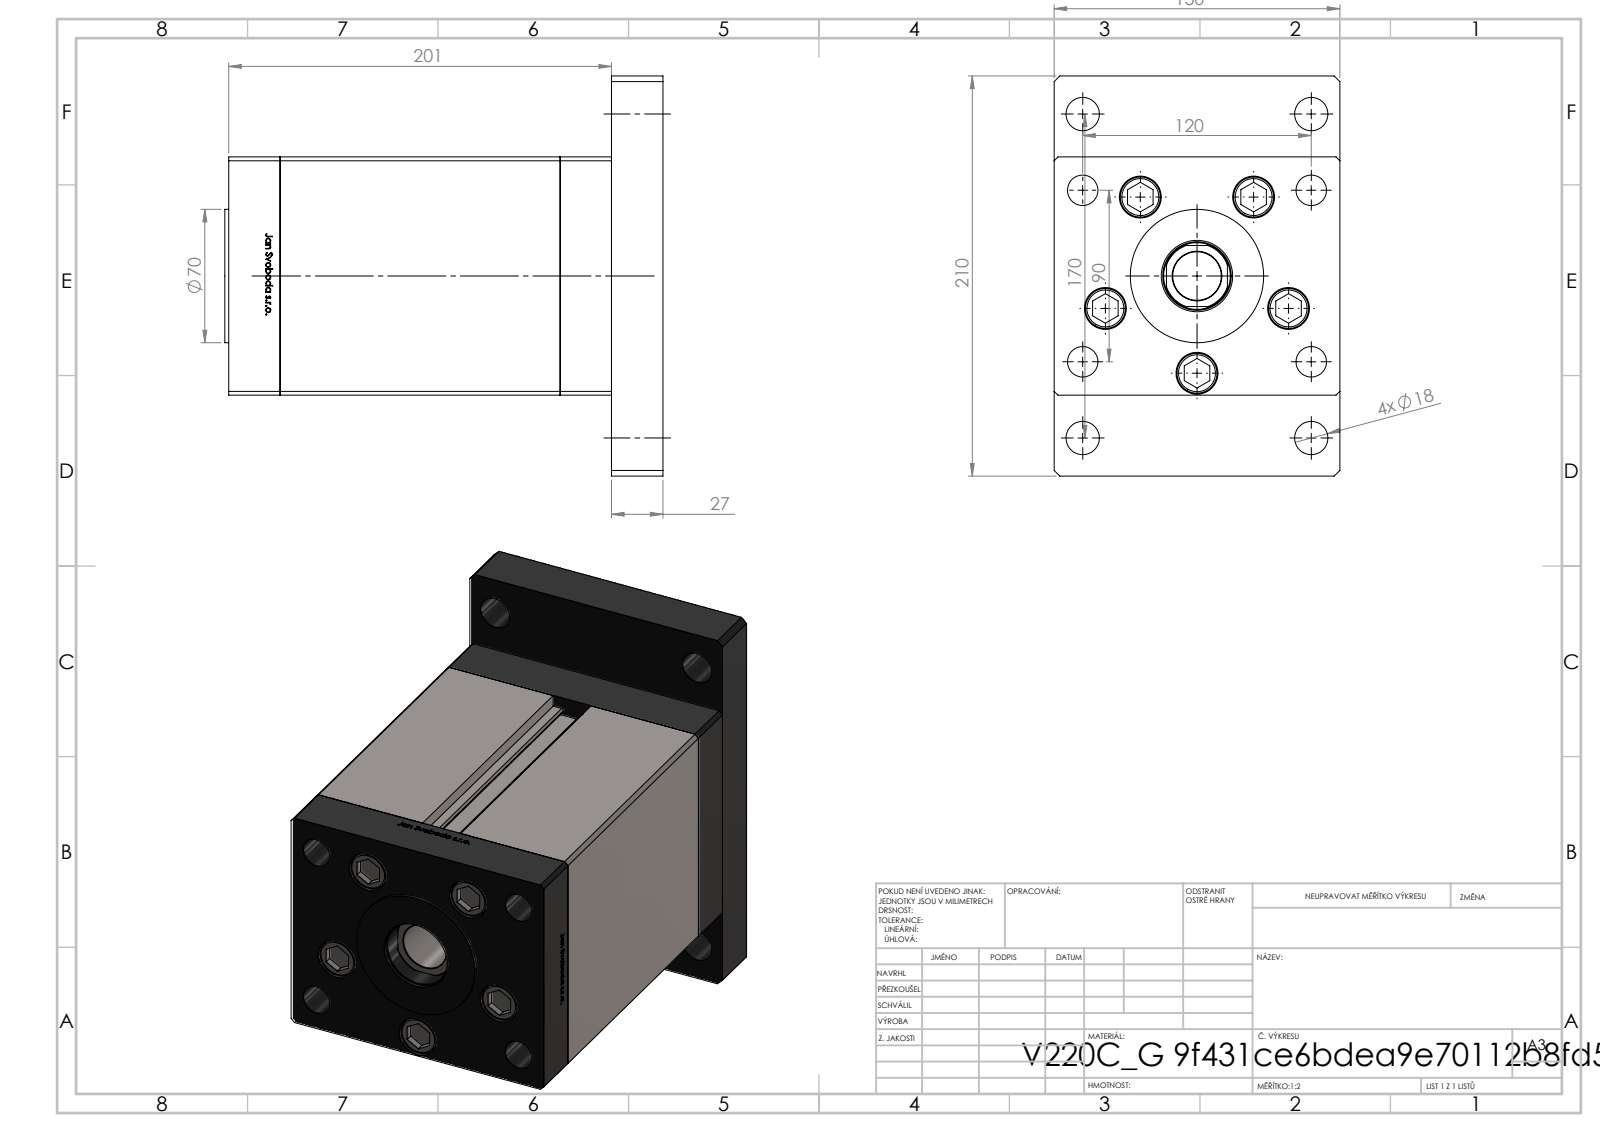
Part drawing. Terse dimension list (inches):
name: ALLEN BOLT; V220C_FRONT_G; V220C_VC_G; V220C_F (+2 more)
written by: SolidWorks 2019 (CONFIG_CONTROL_DESIGN)
unit: in
bodies: 19 solids, 1313 faces (518 planar, 189 cylindrical, 606 other)
size: 9.055 × 8.268 × 5.906
volume: 242.7 in³; area: 686.8 in²
holes: 9× ⌀0.63, 9× ⌀0.689, 5× ⌀0.866, 4× ⌀0.827, 2× ⌀0.079, 2× ⌀0.518, 1× ⌀1.004, 1× ⌀1.417, 1× ⌀1.476, 1× ⌀4.016
bosses: 9× ⌀0.315, 5× ⌀0.827, 1× ⌀3.15, 1× ⌀2.756
rounds: 2× R0.037, 1× R0.689
face distances: 1.063, 7.913, 6.85, 5.906, 4.921, 5.787, 2.126, 0.079, 8.976, 7.835
hole spacings: 2.008, 1.575, 2.953, 4.096, 4.724, 4.98, 5.118, 6.965
